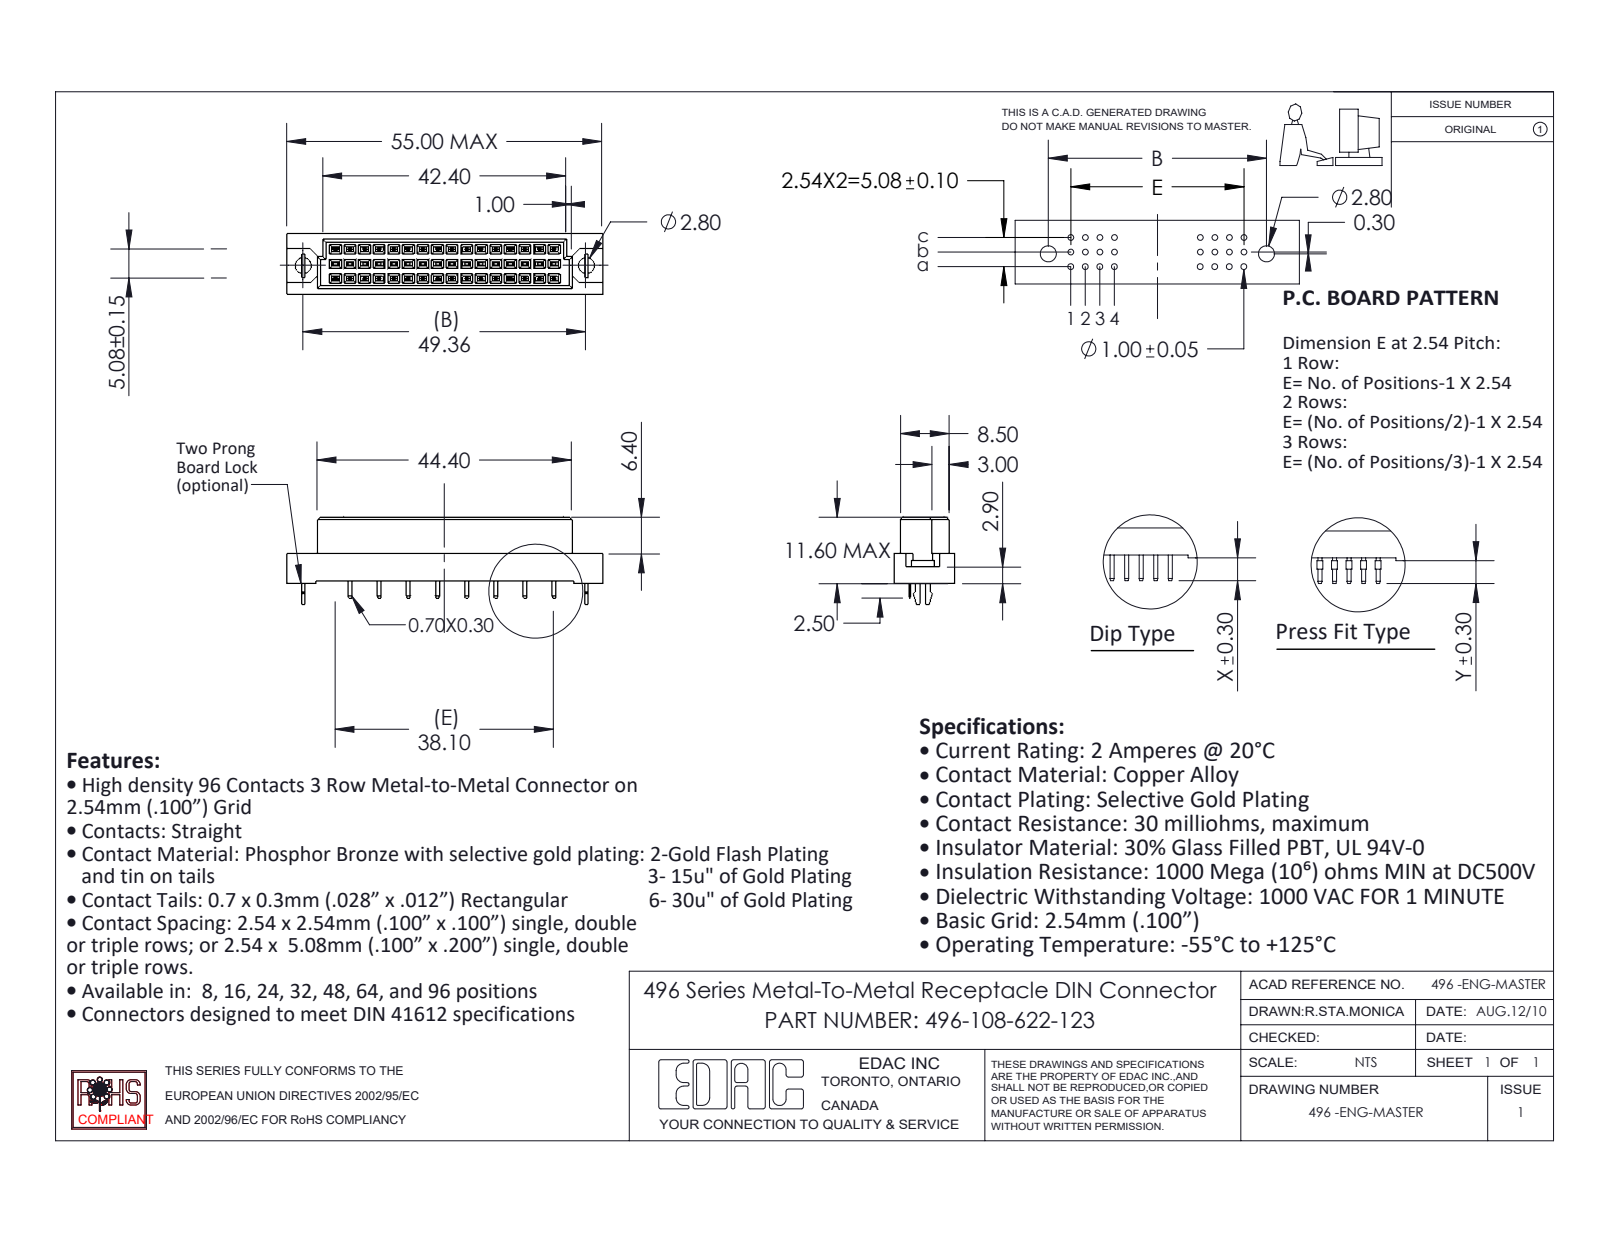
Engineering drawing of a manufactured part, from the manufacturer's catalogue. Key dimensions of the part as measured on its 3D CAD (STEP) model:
Part name (STEP PRODUCT): 496 Part_48; 496 Bore-lock; 496-290_22; 496-108-622-123
STEP written by: SolidWorks 2020 (CONFIG_CONTROL_DESIGN)
Units: millimetres
Bodies: 11 solids, 782 faces (776 planar, 6 cylindrical, 0 other)
Overall size (bounding box): 55 × 15.2 × 10.6
Volume: 4 624 mm³ · Surface area: 4 447 mm²
Round holes (diameter × count): ⌀2.8 ×2
Partial cylindrical surfaces — rounded edges, fillets, slot ends (radius × count): R0.53 ×1
Main face-to-face distances: 2.54, 1.05, 9.55, 5.08, 0.81, 10.6, 3.35, 1.73, 8.5, 0.56
Hole centre spacings: 49.36
